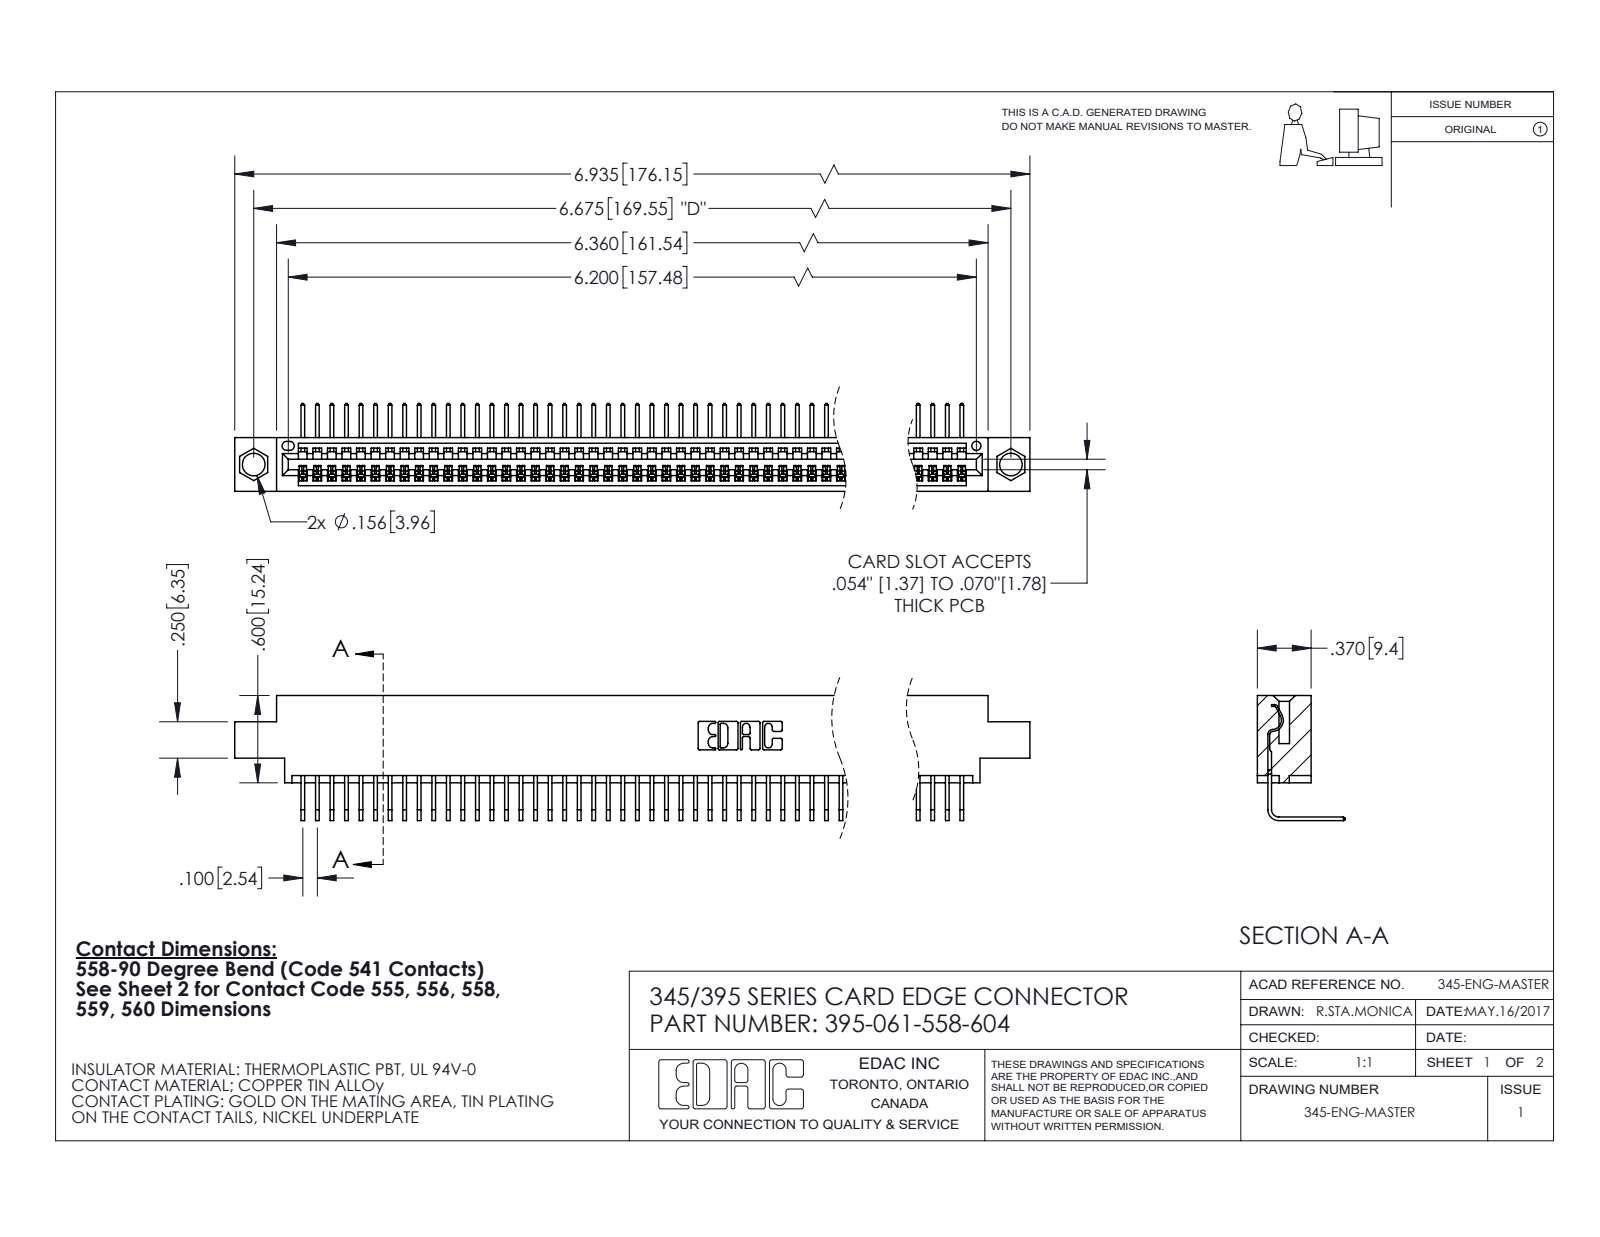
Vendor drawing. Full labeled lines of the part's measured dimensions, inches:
Part name (STEP PRODUCT): 345-292-001_558 Tail - 2; 345 Part_0.170 Offset - 0.156 Dia-TI; 395-061-558-604
STEP written by: SolidWorks 2020 (CONFIG_CONTROL_DESIGN)
Units: inches
Bodies: 62 solids, 3804 faces (2660 planar, 1144 cylindrical, 0 other)
Overall size (bounding box): 6.935 × 0.859 × 0.605
Volume: 1.029 in³ · Surface area: 36.95 in²
Round holes (diameter × count): ⌀0.156 ×2, ⌀0.064 ×1
Partial cylindrical surfaces — rounded edges, fillets, slot ends (radius × count): R0.006 ×122, R0.01 ×22, R0.007 ×6, R0.031 ×6, R0.026 ×3, R0.031 ×2, R0.04 ×2, R0.014 ×1
Main face-to-face distances: 0.072, 0.298, 0.37, 0.2, 0.098, 0.272, 0.025, 0.225, 0.175, 0.149
Hole centre spacings: 0.27, 6.439, 6.675
